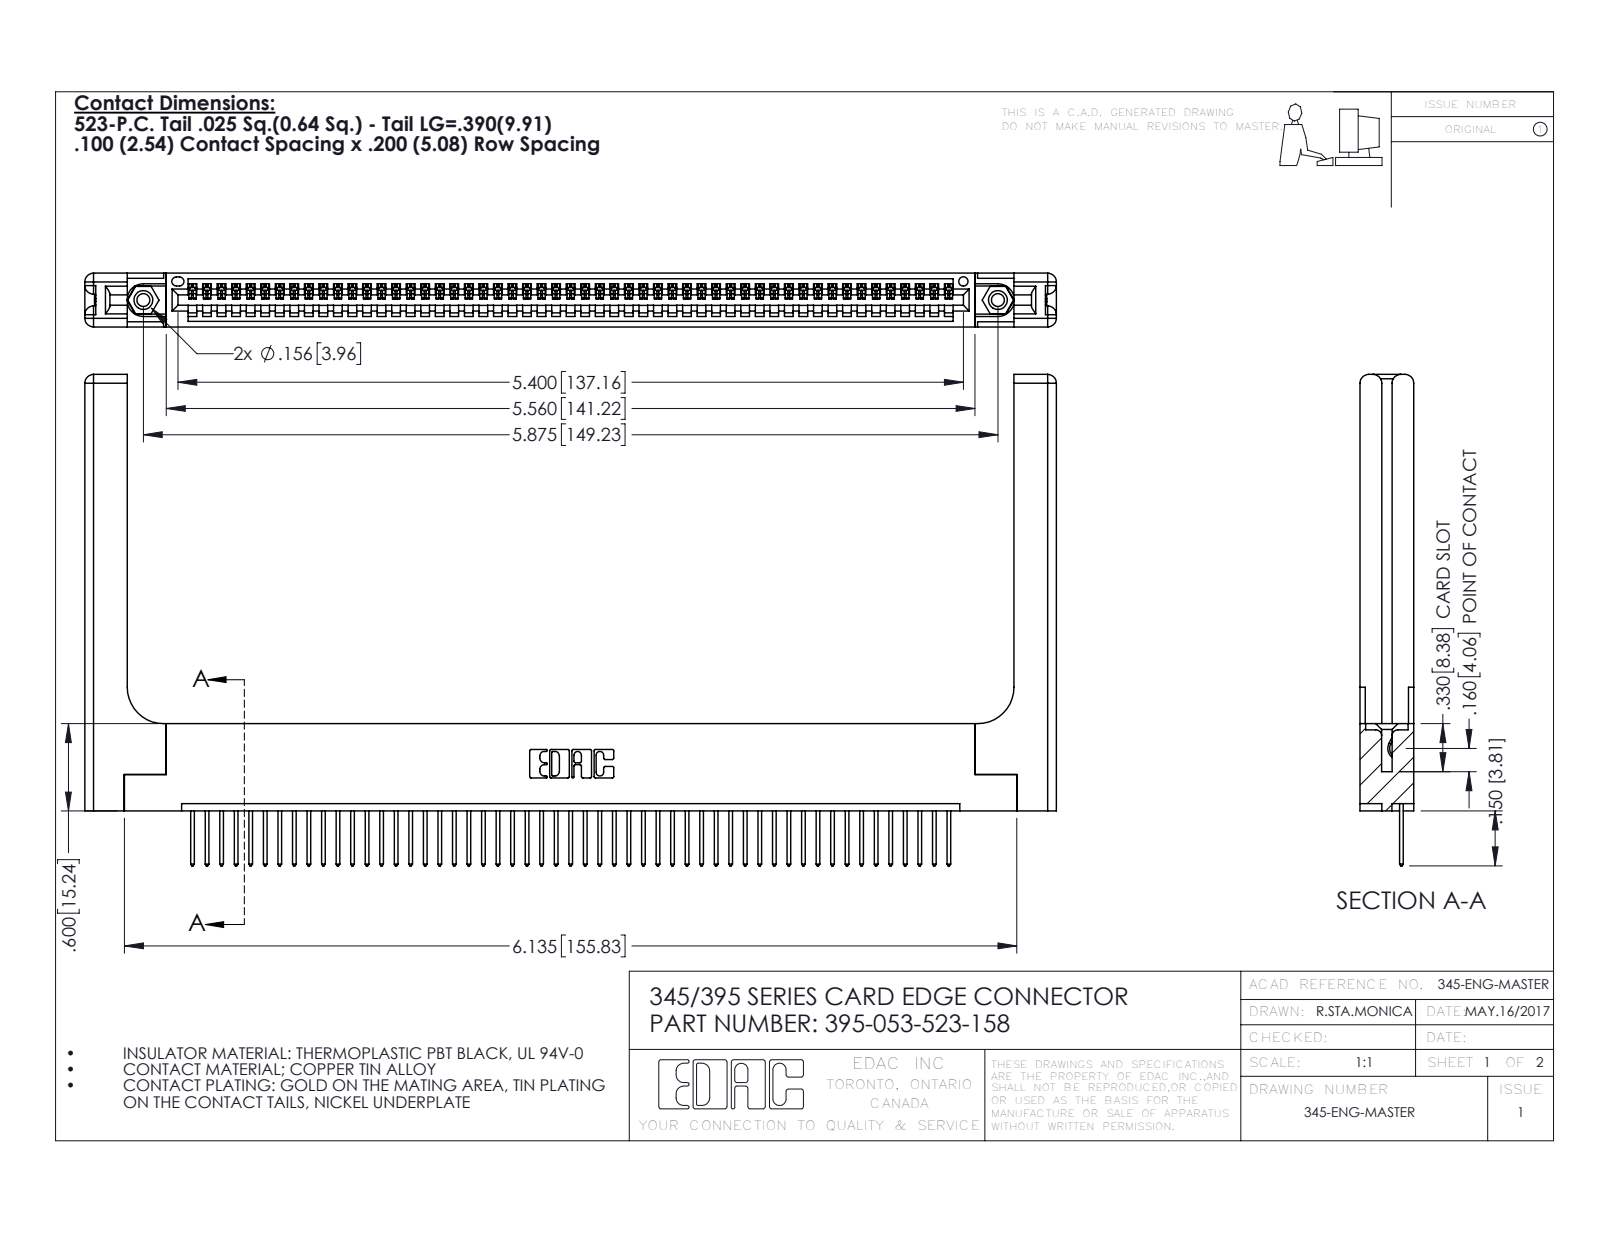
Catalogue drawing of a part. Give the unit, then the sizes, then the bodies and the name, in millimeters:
Units: millimetres
Overall size (bounding box): 169.6 × 85.8 × 9.4
Round holes (diameter × count): ⌀2.3 ×2, ⌀3.2 ×2, ⌀4 ×2, ⌀1.6 ×1
Round bosses / shafts (diameter × count): ⌀3.9 ×2
Partial cylindrical surfaces — rounded edges, fillets, slot ends (radius × count): R0.2 ×106, R0.3 ×106, R0.3 ×22, R1.5 ×16, R0.2 ×6, R0.8 ×6, R0.7 ×3, R0.8 ×2
Main face-to-face distances: 1.8, 9.4, 7.6, 5.1, 2.5, 6.9, 0.6, 5.7, 3.8, 3.8
Hole centre spacings: 6.9, 143.2, 149.2
Volume: 24 700 mm³ · Surface area: 27 020 mm²
Bodies: 58 solids, 3456 faces (2348 planar, 1048 cylindrical, 60 other)
Part name (STEP PRODUCT): 345 Part_Flush Mounting Lugs - 0.156 Dia-TH; 345-292-001_345-293-123; 395-053-523-158; 345-250-001_345-250-001-102 (+1 more)
STEP written by: SolidWorks 2016 (CONFIG_CONTROL_DESIGN)
